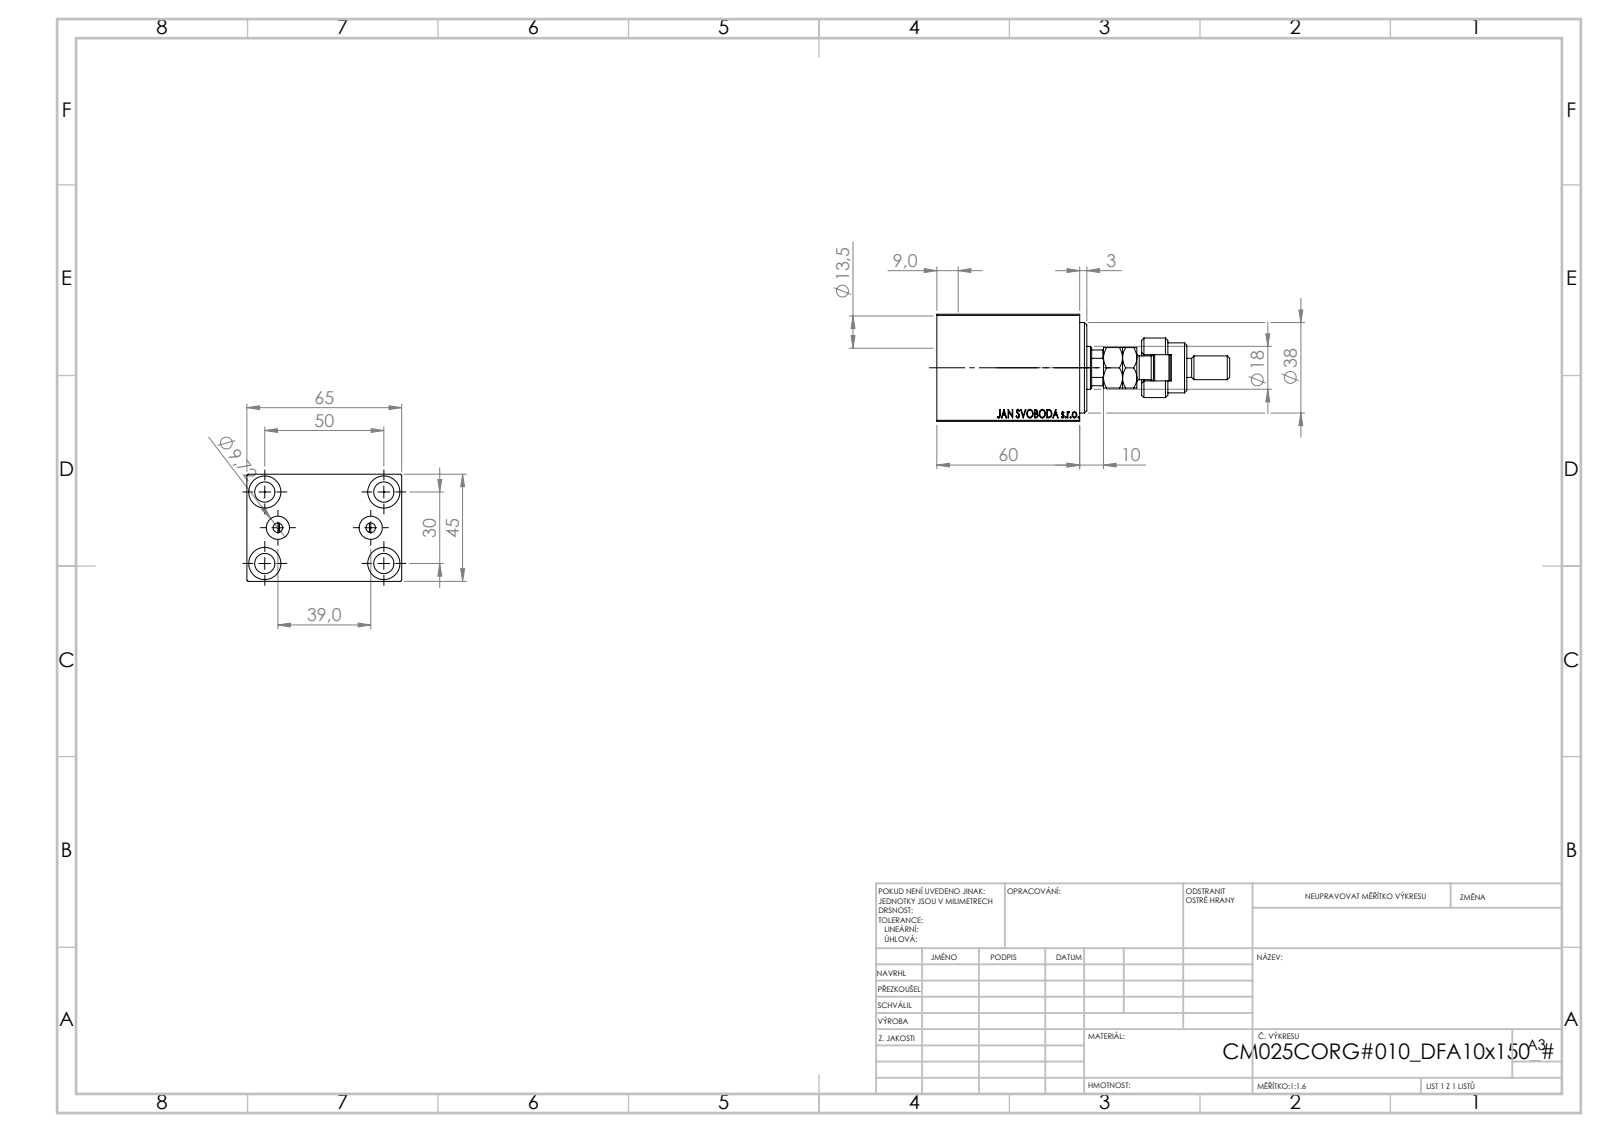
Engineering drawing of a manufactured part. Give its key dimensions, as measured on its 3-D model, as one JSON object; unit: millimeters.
{"part_name": "V450CM_C_Body; V450CM_VC_B; FEMALE_PART_FOR_DFA; MFA (+1 more)", "step_written_by": "SolidWorks 2019 (CONFIG_CONTROL_DESIGN)", "units": "millimeters", "bodies": {"solids": 5, "faces": 943, "planar": 436, "cylindrical": 69, "other": 438}, "overall_size": [123, 65, 45], "volume_mm3": 166172, "surface_area_mm2": 48310, "round_holes": [[8.5, 5], [13.5, 4], [4, 2], [9.72, 2], [18, 1], [21.5, 1], [27, 1], [38, 1]], "round_bosses_or_shafts": [[25, 1], [21, 1], [16, 1], [10, 1], [8, 1]], "partial_cylinders_radius": [[5.5, 1], [8.5, 1], [8.75, 1]], "face_to_face_distances": [45, 65, 9, 51, 5, 60, 46, 55, 54, 3], "hole_center_spacings": [15.98, 29.15, 46.96, 19.5, 30, 50, 58.31, 39]}
